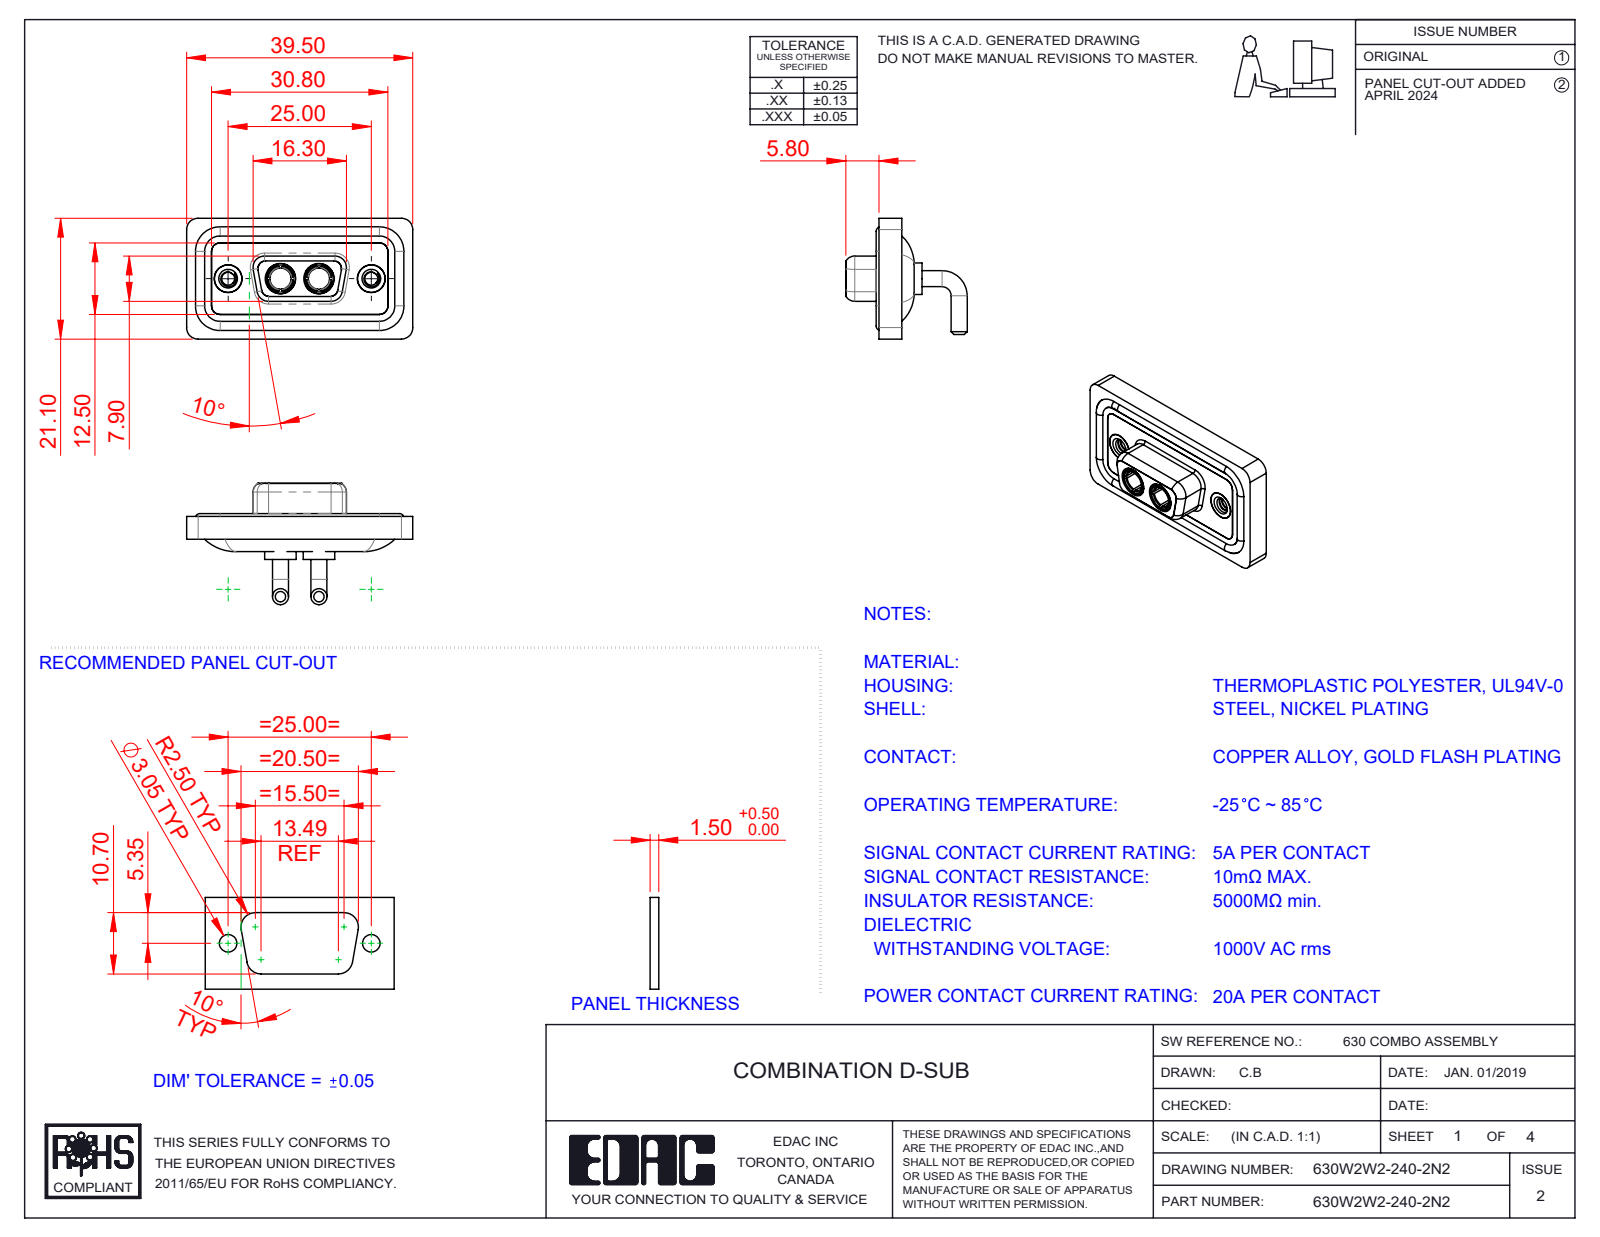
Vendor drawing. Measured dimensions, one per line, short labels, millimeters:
name: 630W2W2-240-2N2; 630Combo Waterproof Housing_09 Contacts; 630Combo Threaded Rivet_2; Power Socket_20A RA (+3 more)
written by: SolidWorks 2023 (CONFIG_CONTROL_DESIGN)
unit: mm
bodies: 11 solids, 542 faces (163 planar, 238 cylindrical, 141 other)
size: 39.5 × 21.2 × 21.1
volume: 4 816 mm³; area: 7 786 mm²
holes: 4× ⌀4.85, 2× ⌀2.26, 2× ⌀3.7, 2× ⌀4, 2× ⌀4.05, 2× ⌀5, 2× ⌀5.3
bosses: 4× ⌀2.8, 4× ⌀1.6, 2× ⌀5.5, 2× ⌀5.2, 2× ⌀4.96, 2× ⌀4.95, 2× ⌀4.8, 2× ⌀4.75
rounds: 18× R1.5, 18× R2, 8× R1.35, 8× R1.6, 4× R0.25, 4× R0.5, 4× R0.6, 4× R0.65
face distances: 0.4, 1.8, 1.1, 2.9, 2.5, 1.6, 3.1, 1.5, 2.1, 0.5
hole spacings: 9.14, 15.86, 6.72, 25
